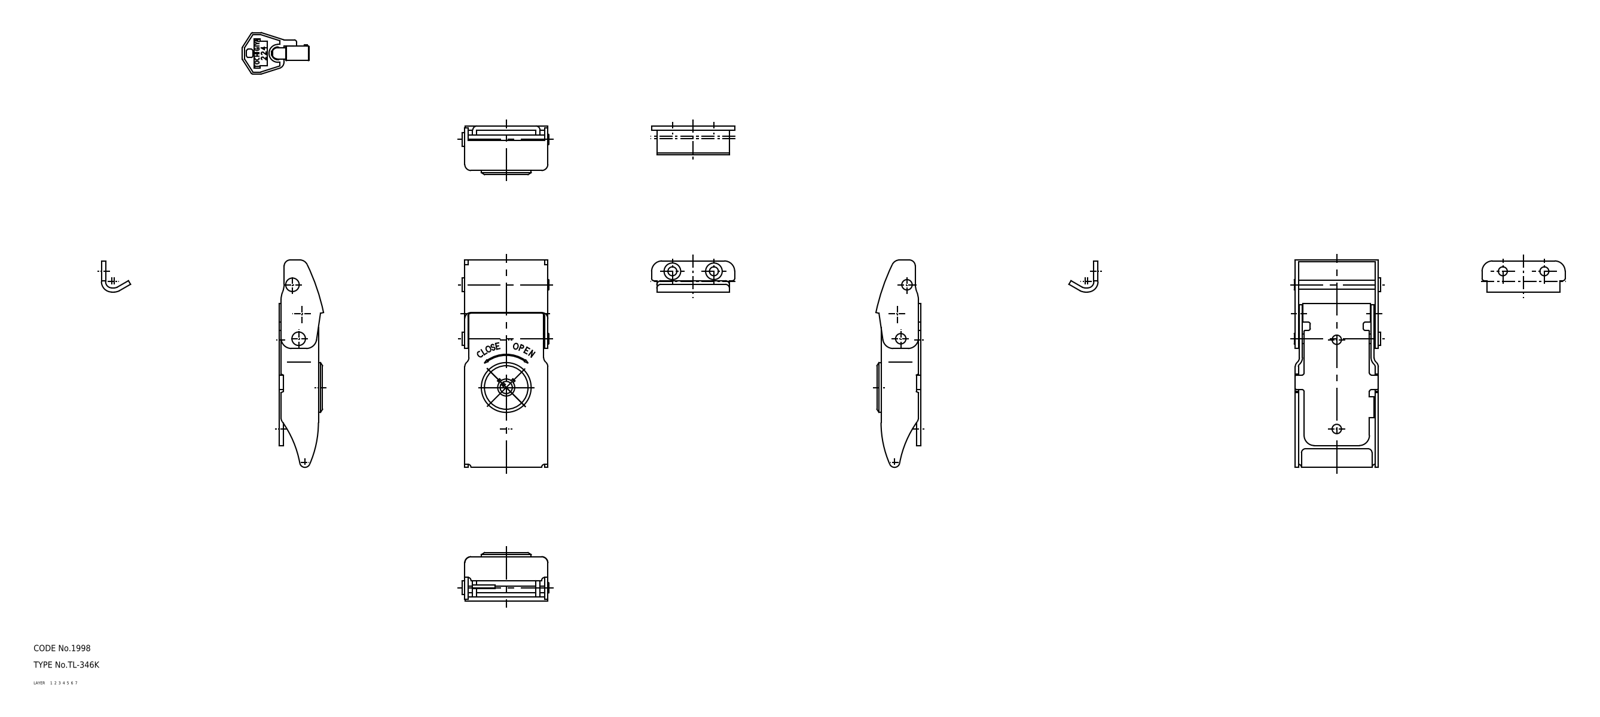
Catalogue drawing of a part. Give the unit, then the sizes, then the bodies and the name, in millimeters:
Units: millimetres
Overall size (bounding box): 100 × 70 × 41.7
Volume: 26 089 mm³ · Surface area: 30 585 mm²
Bodies: 9 solids, 404 faces (0 planar, 0 cylindrical, 404 other)
Part name (STEP PRODUCT): shaft_B; shaft_A; lock; lever (+5 more)
STEP written by: CADfix (AUTOMOTIVE_DESIGN)
